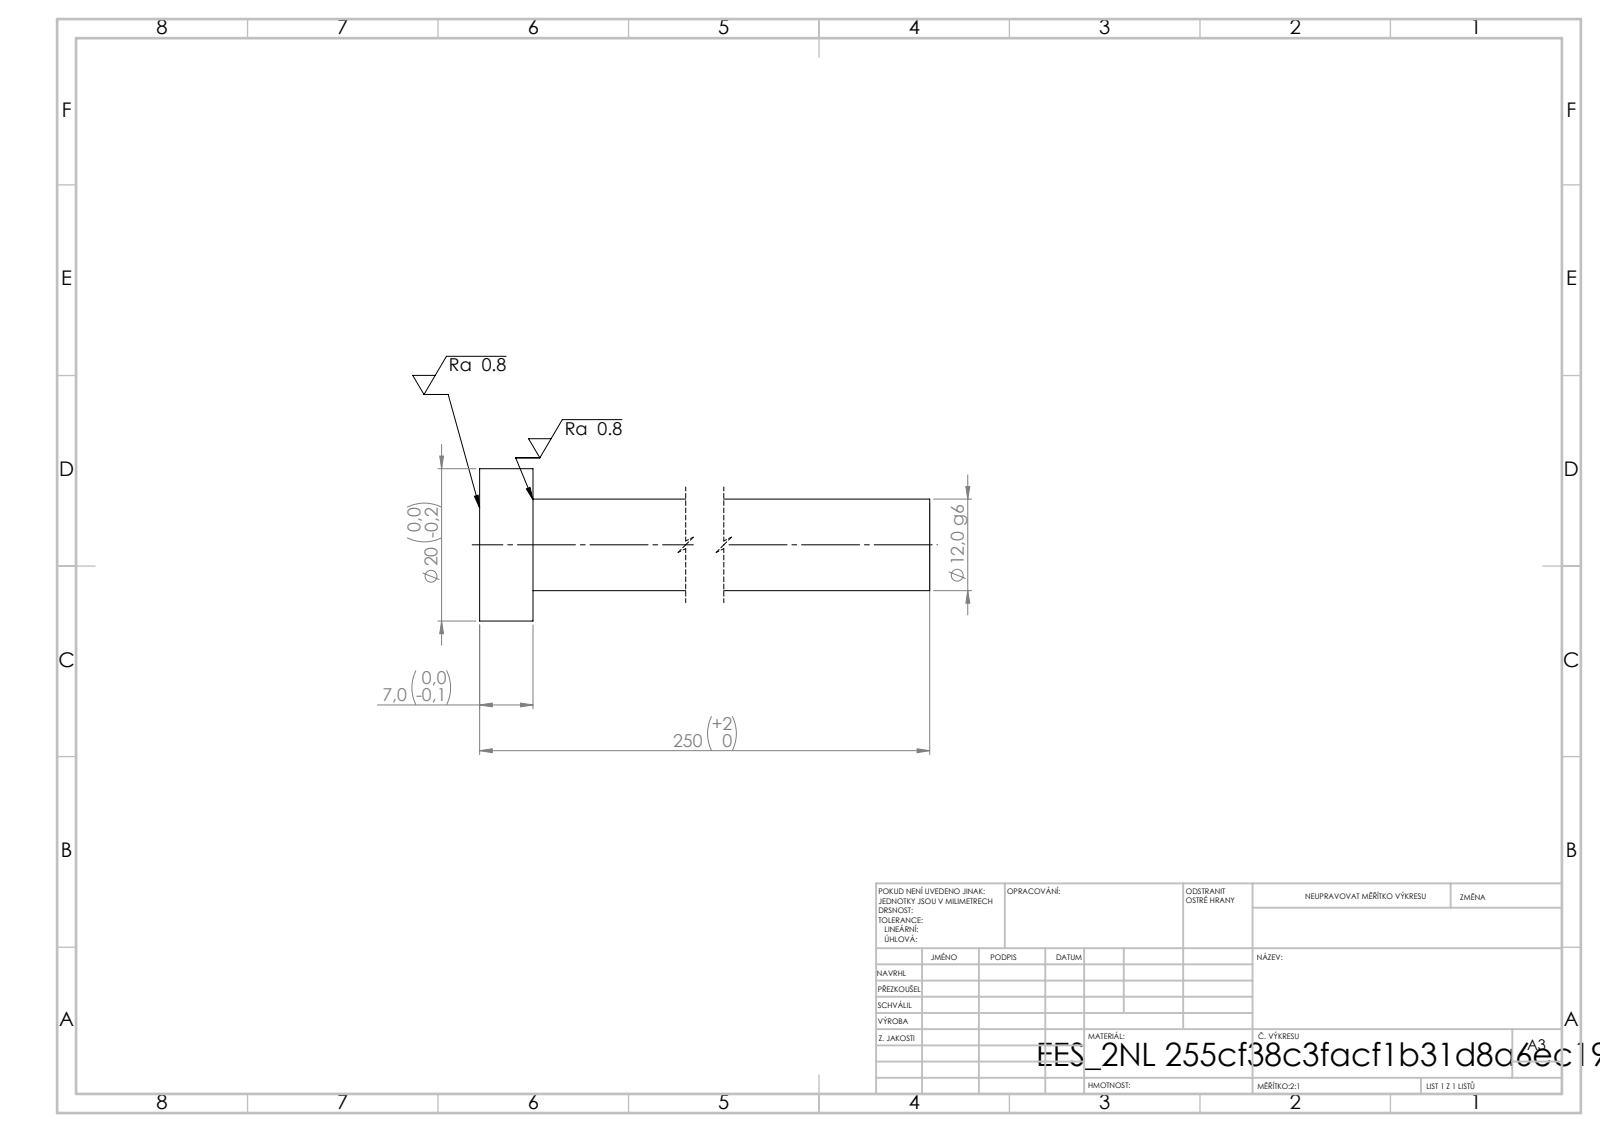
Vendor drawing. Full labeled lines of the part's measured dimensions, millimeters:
STEP written by: SolidWorks 2019 (CONFIG_CONTROL_DESIGN)
Units: millimetres
Bodies: 1 solid, 7 faces (3 planar, 4 cylindrical, 0 other)
Overall size (bounding box): 250 × 20 × 20
Volume: 29 682 mm³ · Surface area: 10 229 mm²
Round bosses / shafts (diameter × count): ⌀20 ×1, ⌀12 ×1
Main face-to-face distances: 7, 250, 243
